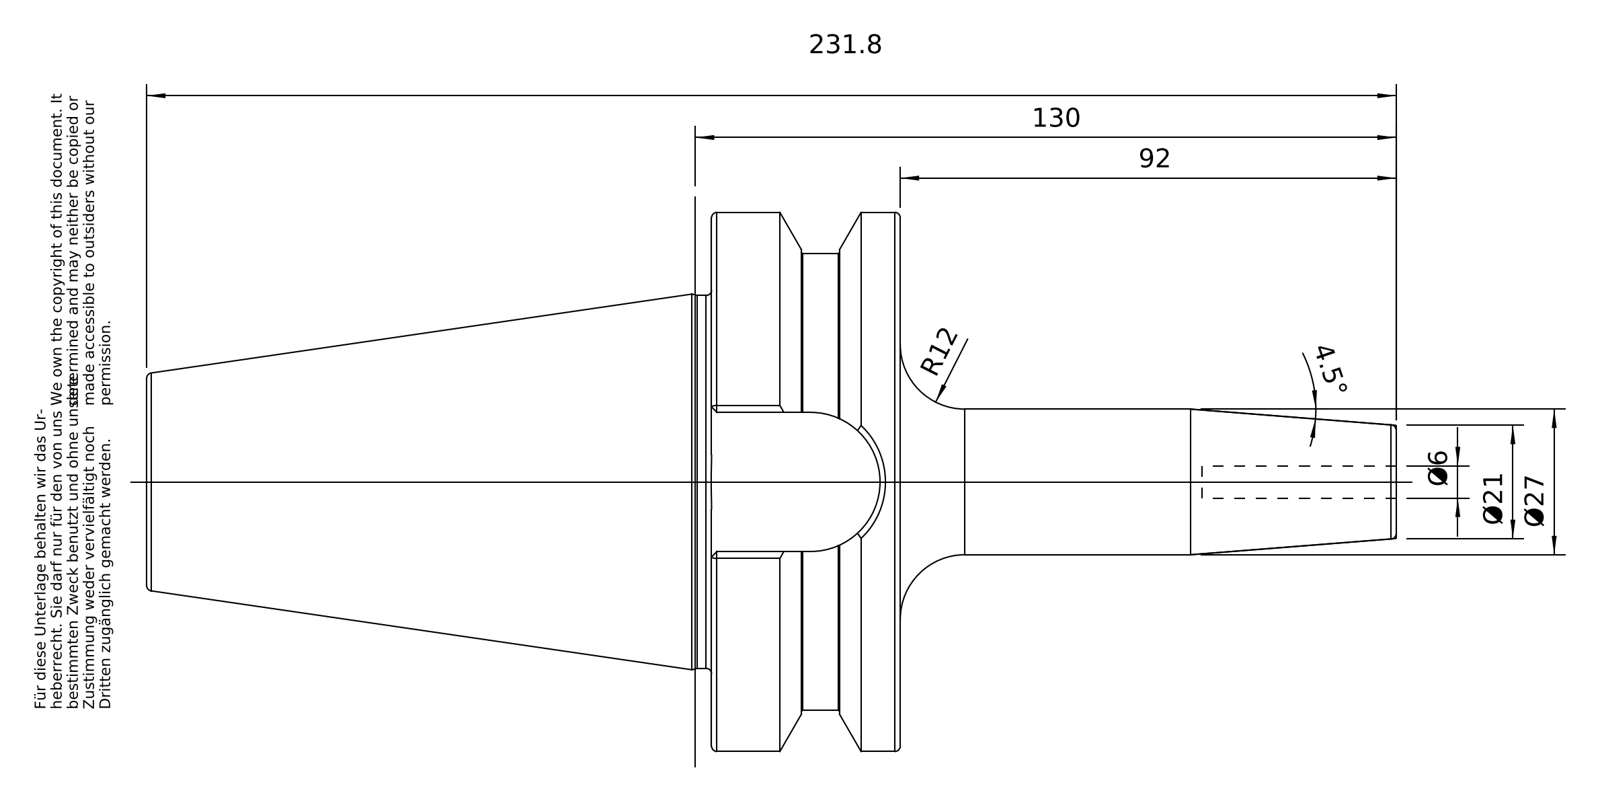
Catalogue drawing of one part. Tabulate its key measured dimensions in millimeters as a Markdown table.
| quantity | value |
| --- | --- |
| part name | 50-644-06 |
| STEP written by | PRO/ENGINEER BY PARAMETRIC TECHNOLOGY CORPORATION, 2010430 (CONFIG_CONTROL_DESIGN) |
| units | millimeters |
| bodies | 1 solid, 96 faces (26 planar, 22 cylindrical, 48 other) |
| overall size | 231.8 × 99.97 × 99.97 |
| volume | 518 343 mm³ |
| surface area | 59 357 mm² |
| round holes (diameter × count) | 6 × 1, 20.75 × 1, 25.02 × 1, 25.7 × 1 |
| round bosses / shafts (diameter × count) | 99.97 × 1, 84.75 × 1, 69.15 × 1, 27 × 1, 24.01 × 1 |
| partial cylindrical surfaces (radius × count) | 12.9 × 1 |
| main face-to-face distances | 35, 70.4, 104.8, 139.8, 25.8, 231.8, 127, 92, 48, 56.8 |
